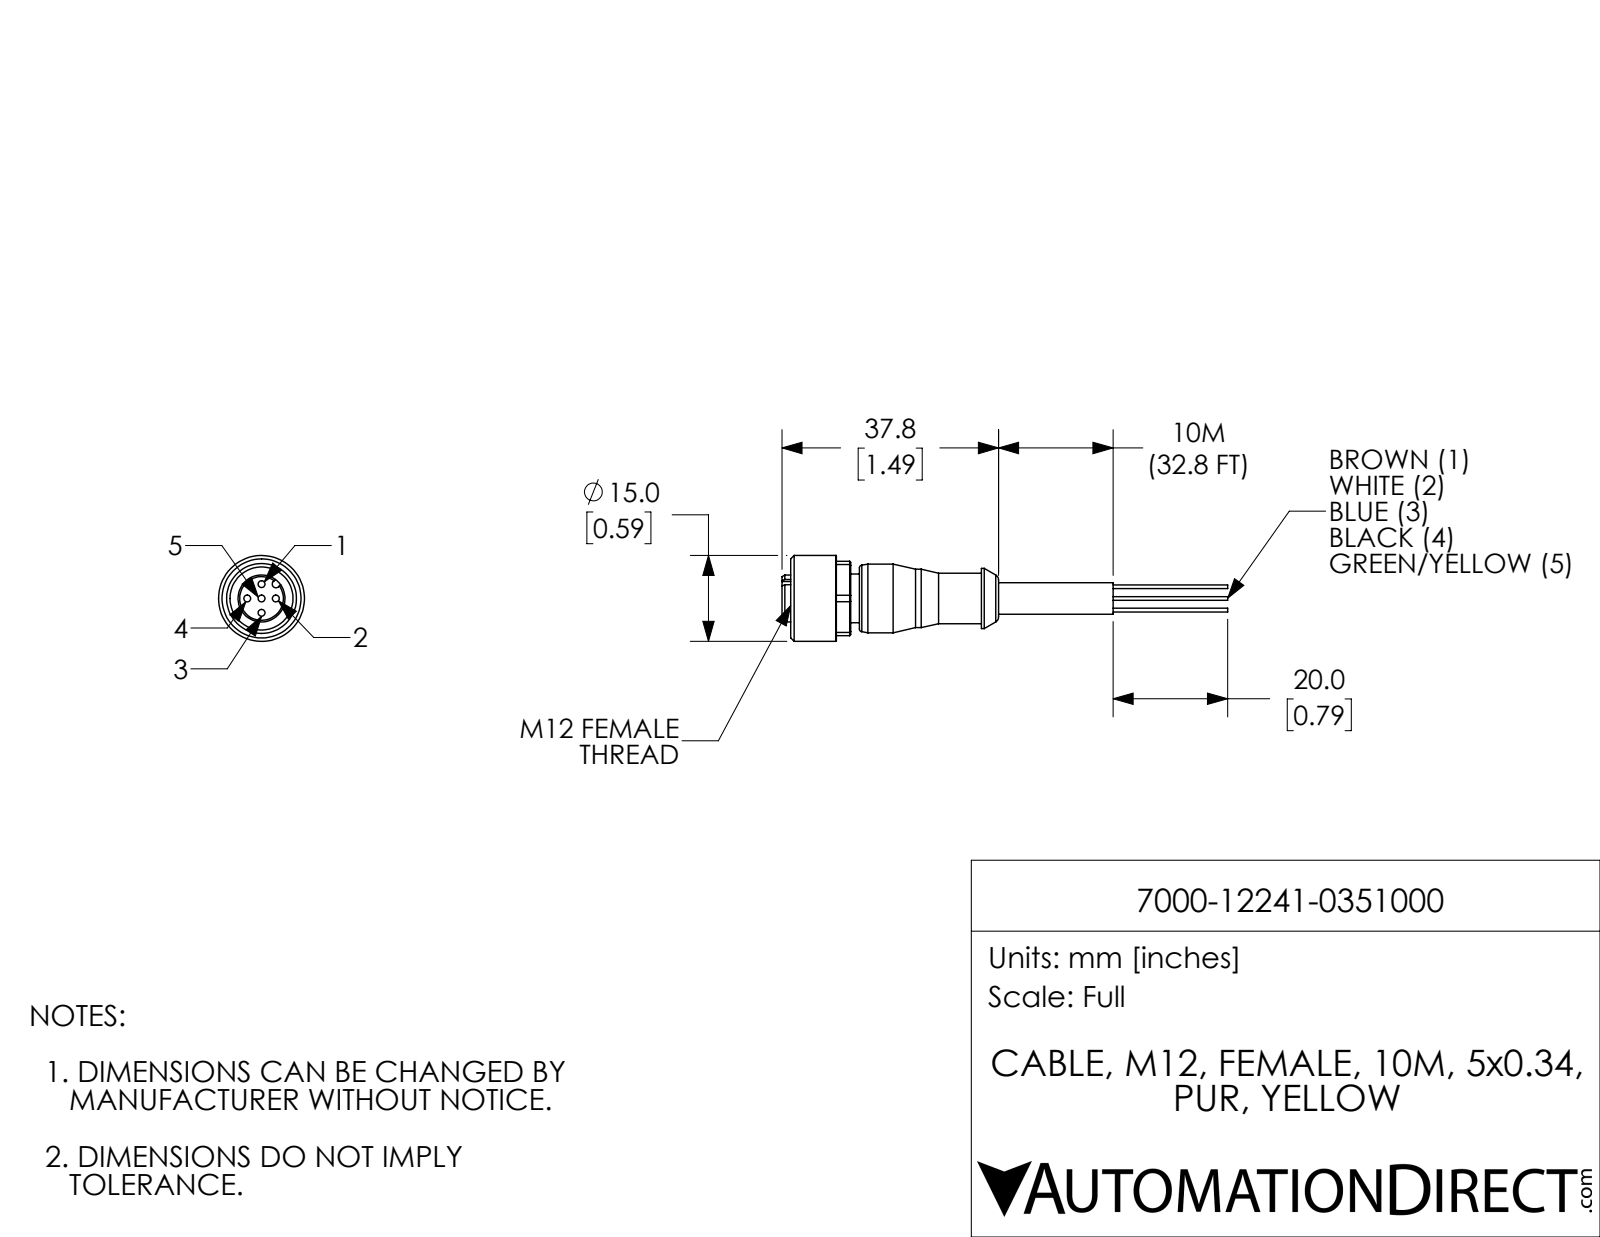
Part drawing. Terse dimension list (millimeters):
name: 7000-12241-0351000
written by: SolidWorks 2021 (CONFIG_CONTROL_DESIGN)
unit: mm
bodies: 1 solid, 106 faces (34 planar, 45 cylindrical, 27 other)
size: 77.8 × 15 × 15
volume: 4 060 mm³; area: 2 871 mm²
holes: 5× ⌀1.2, 1× ⌀11
bosses: 5× ⌀0.7, 1× ⌀15, 1× ⌀12, 1× ⌀10.5, 1× ⌀10.2, 1× ⌀8.8, 1× ⌀8.5, 1× ⌀8.2
rounds: 1× R0.7, 1× R7.2
face distances: 12, 1.5, 3, 13, 9, 25.8, 7.5, 10.5, 2.5, 13.5
hole spacings: 2.5, 3.5, 5
